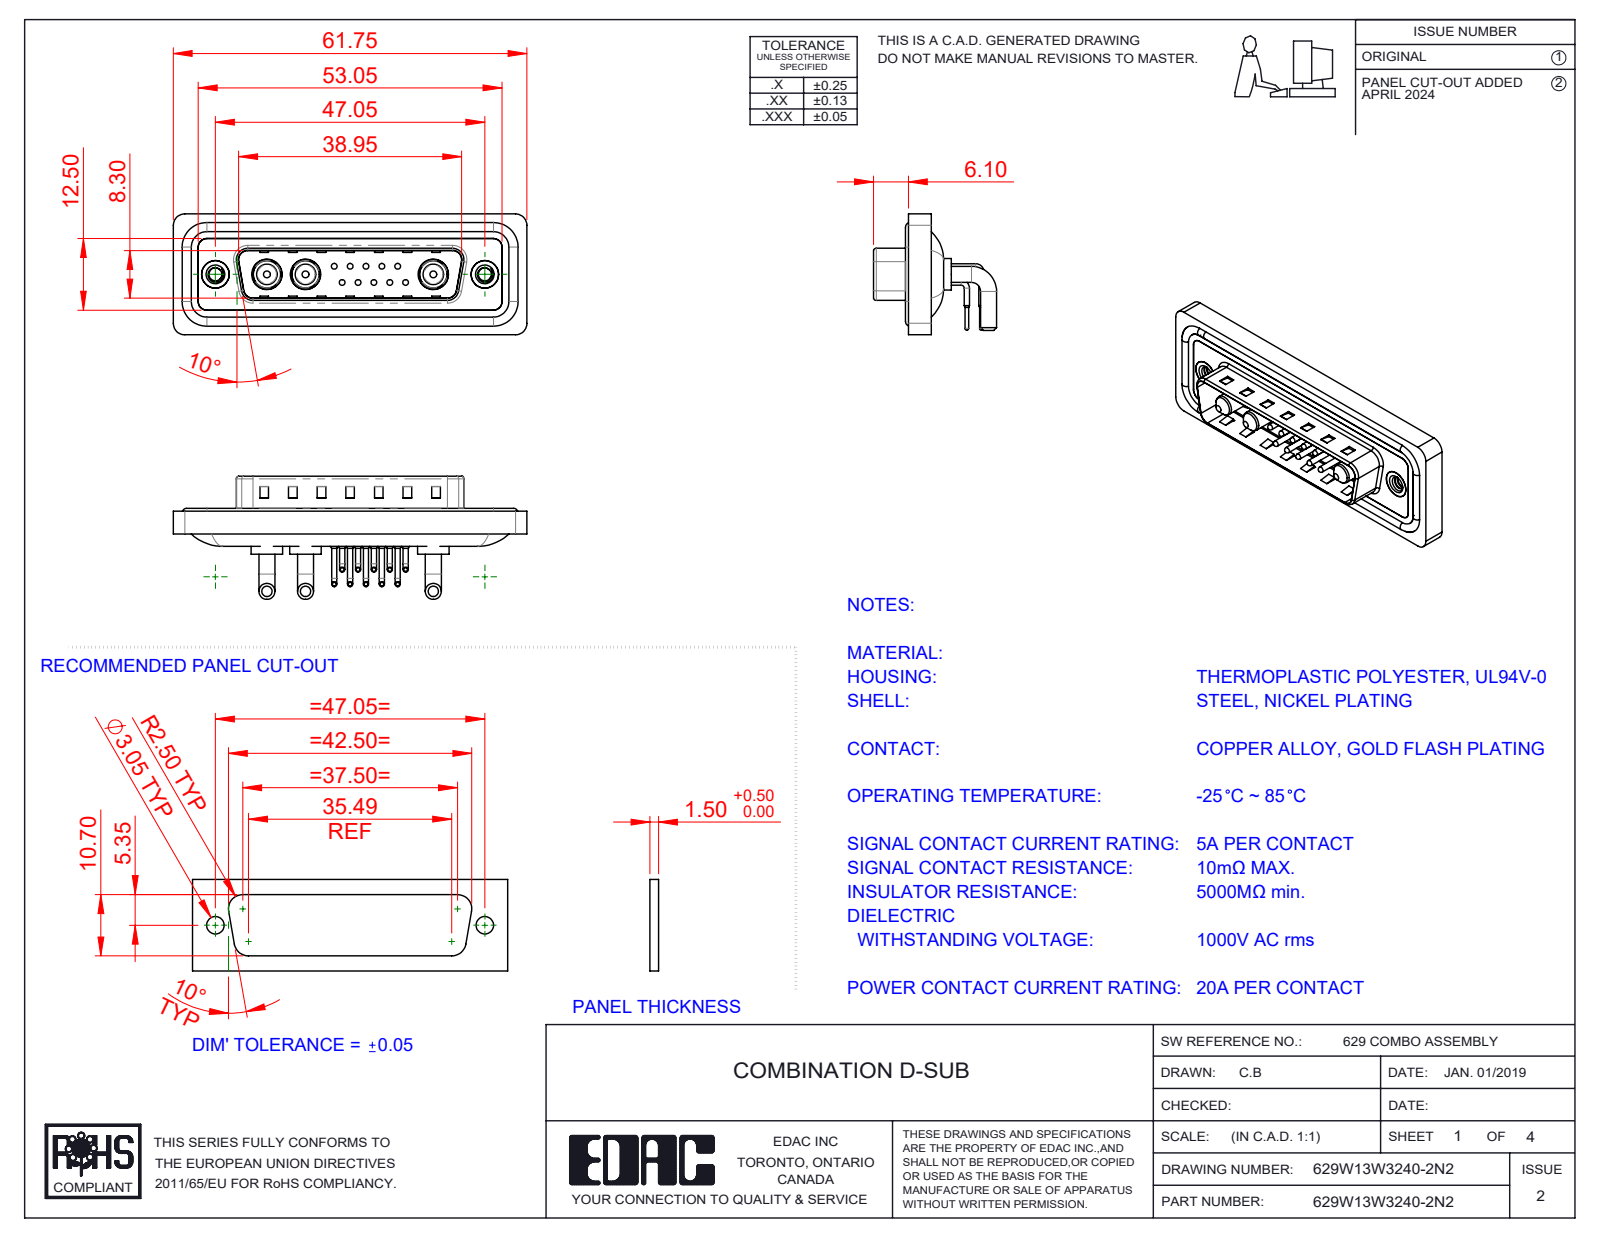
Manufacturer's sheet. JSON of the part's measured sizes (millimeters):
{"part_name": "629Combo Contact Row 2; 629W13W3140-2N2; 629Combo Shell Rear_25 Contacts; 629Combo Contact Row 1 (+5 more)", "step_written_by": "SolidWorks 2023 (CONFIG_CONTROL_DESIGN)", "units": "millimeters", "bodies": {"solids": 23, "faces": 1712, "planar": 879, "cylindrical": 611, "other": 222}, "overall_size": [61.75, 21.5, 21.1], "volume_mm3": 7621, "surface_area_mm2": 12497, "round_holes": [[0.75, 10], [1.6, 10], [2, 10], [4.85, 3], [5.3, 3], [2.26, 2], [4, 2], [4.8, 2], [5, 2]], "round_bosses_or_shafts": [[0.9, 20], [1.5, 10], [1, 10], [0.65, 10], [2.8, 6], [1.6, 4], [5.5, 3], [5.2, 3]], "partial_cylinders_radius": [[1.5, 18], [2, 18], [1.01, 10], [0.5, 8], [1.6, 8], [0.25, 4], [0.6, 4], [0.65, 4]], "face_to_face_distances": [0.4, 2.9, 0.8, 4.1, 1.1, 2.1, 1.6, 4.5, 1.5, 2.5], "hole_center_spacings": [3.16, 2.77, 5.04, 5.54, 7.49, 5.03, 8.31, 10.11]}
